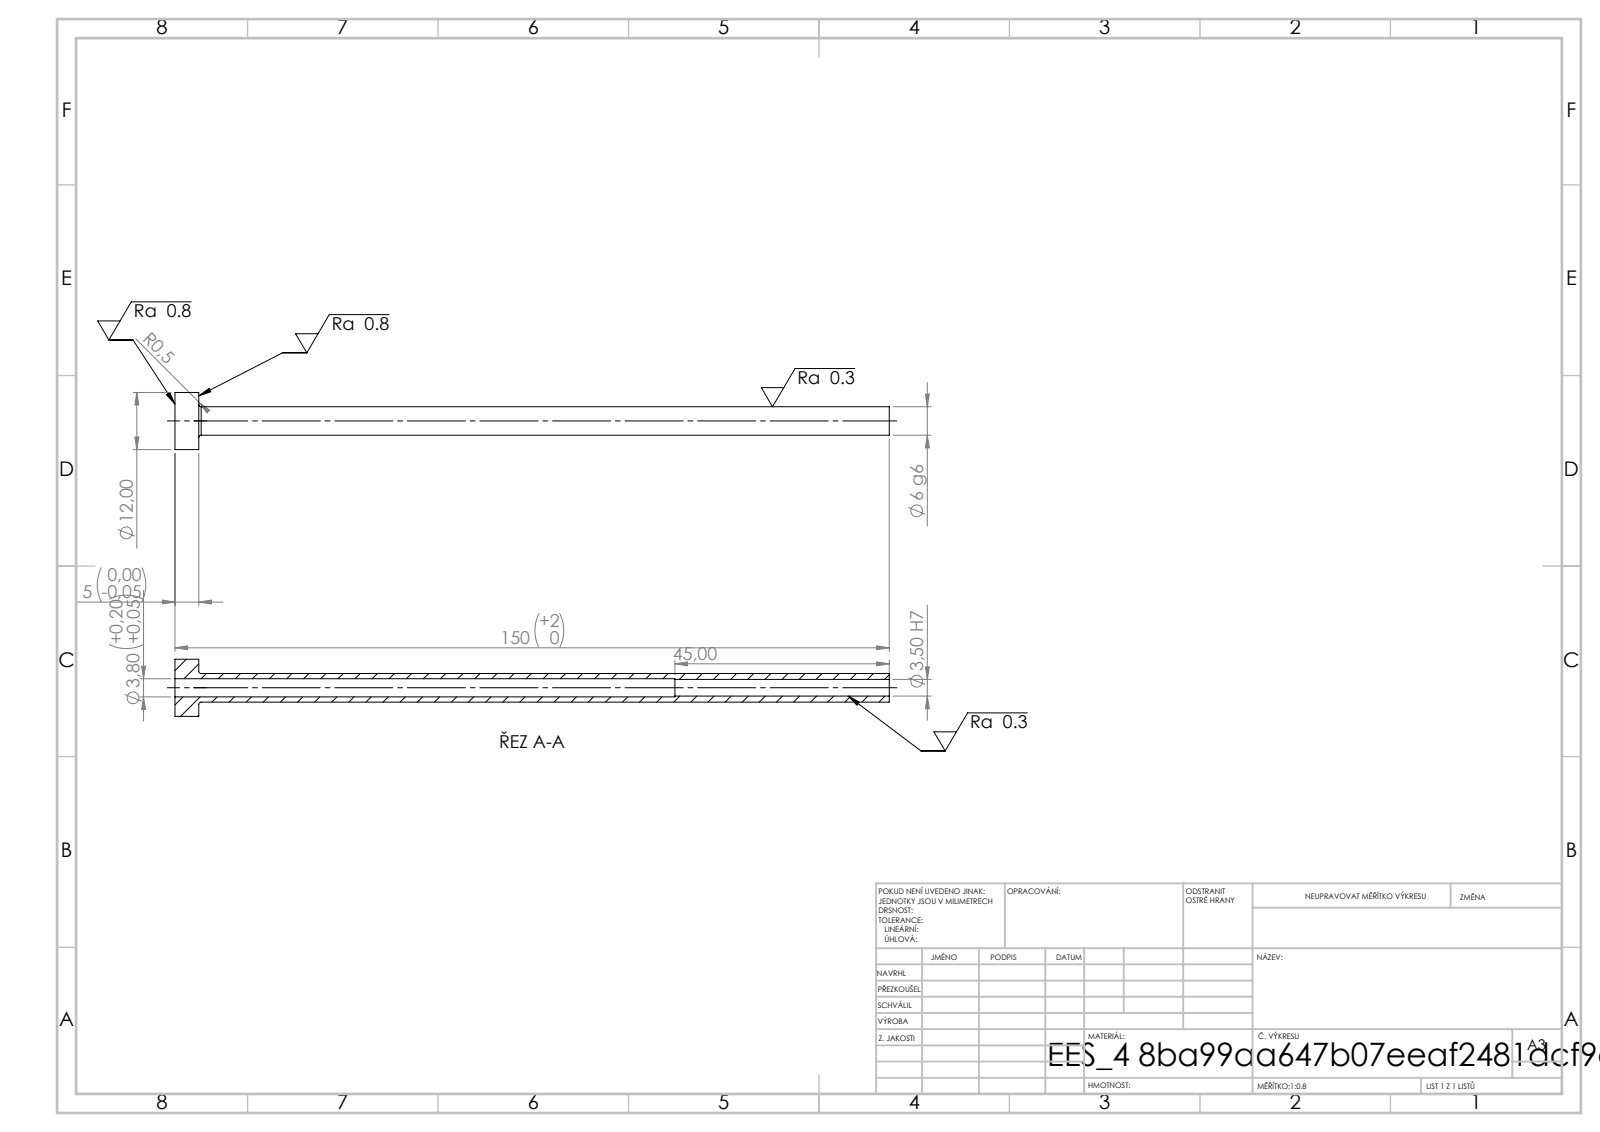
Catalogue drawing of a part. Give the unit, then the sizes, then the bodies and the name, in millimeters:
Units: millimetres
Overall size (bounding box): 150 × 12 × 12
Round holes (diameter × count): ⌀3.5 ×1, ⌀3.8 ×1
Round bosses / shafts (diameter × count): ⌀12 ×1, ⌀6 ×1
Main face-to-face distances: 5, 150, 145, 105, 100, 45
Volume: 3 043 mm³ · Surface area: 4 873 mm²
Bodies: 1 solid, 14 faces (4 planar, 8 cylindrical, 2 other)
STEP written by: SolidWorks 2019 (CONFIG_CONTROL_DESIGN)
